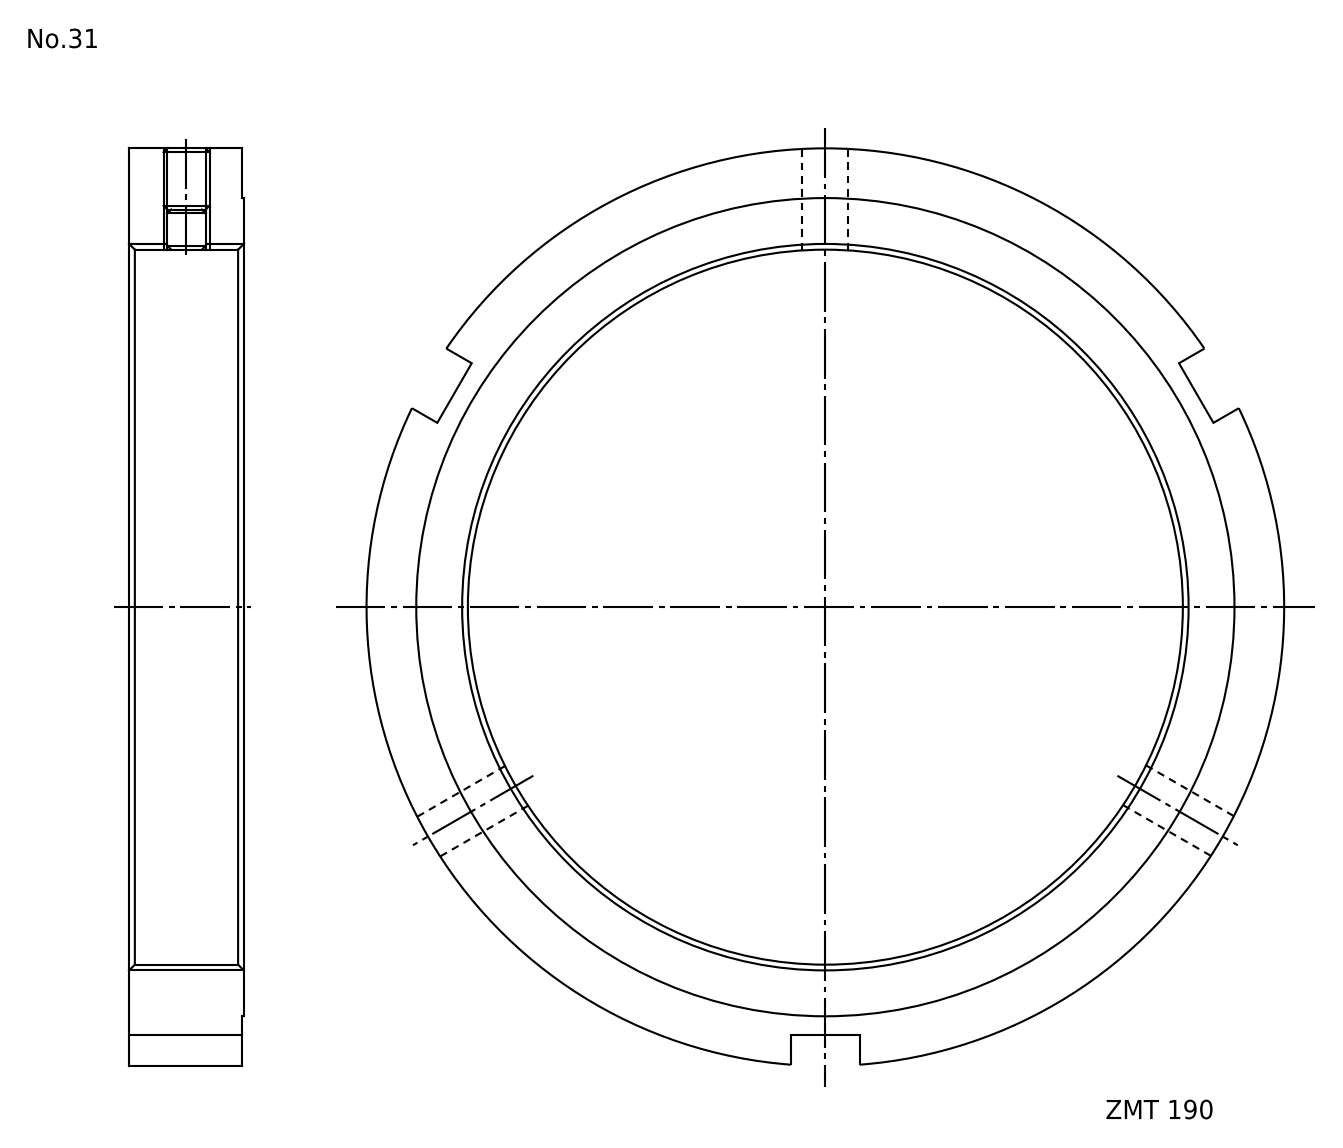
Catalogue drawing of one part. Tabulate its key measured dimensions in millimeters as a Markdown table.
| quantity | value |
| --- | --- |
| part name | FKD ZMT190 |
| STEP written by | Autodesk Inventor LT (CONFIG_CONTROL_DESIGN) |
| units | millimeters |
| bodies | 1 solid, 20 faces (12 planar, 8 cylindrical, 0 other) |
| overall size | 240 × 239.66 × 30 |
| volume | 483 367 mm³ |
| surface area | 76 662 mm² |
| round holes (diameter × count) | 10.11 × 3, 190 × 1 |
| round bosses / shafts (diameter × count) | 240 × 1, 214 × 1 |
| main face-to-face distances | 29.5, 0.5, 30, 18 |
